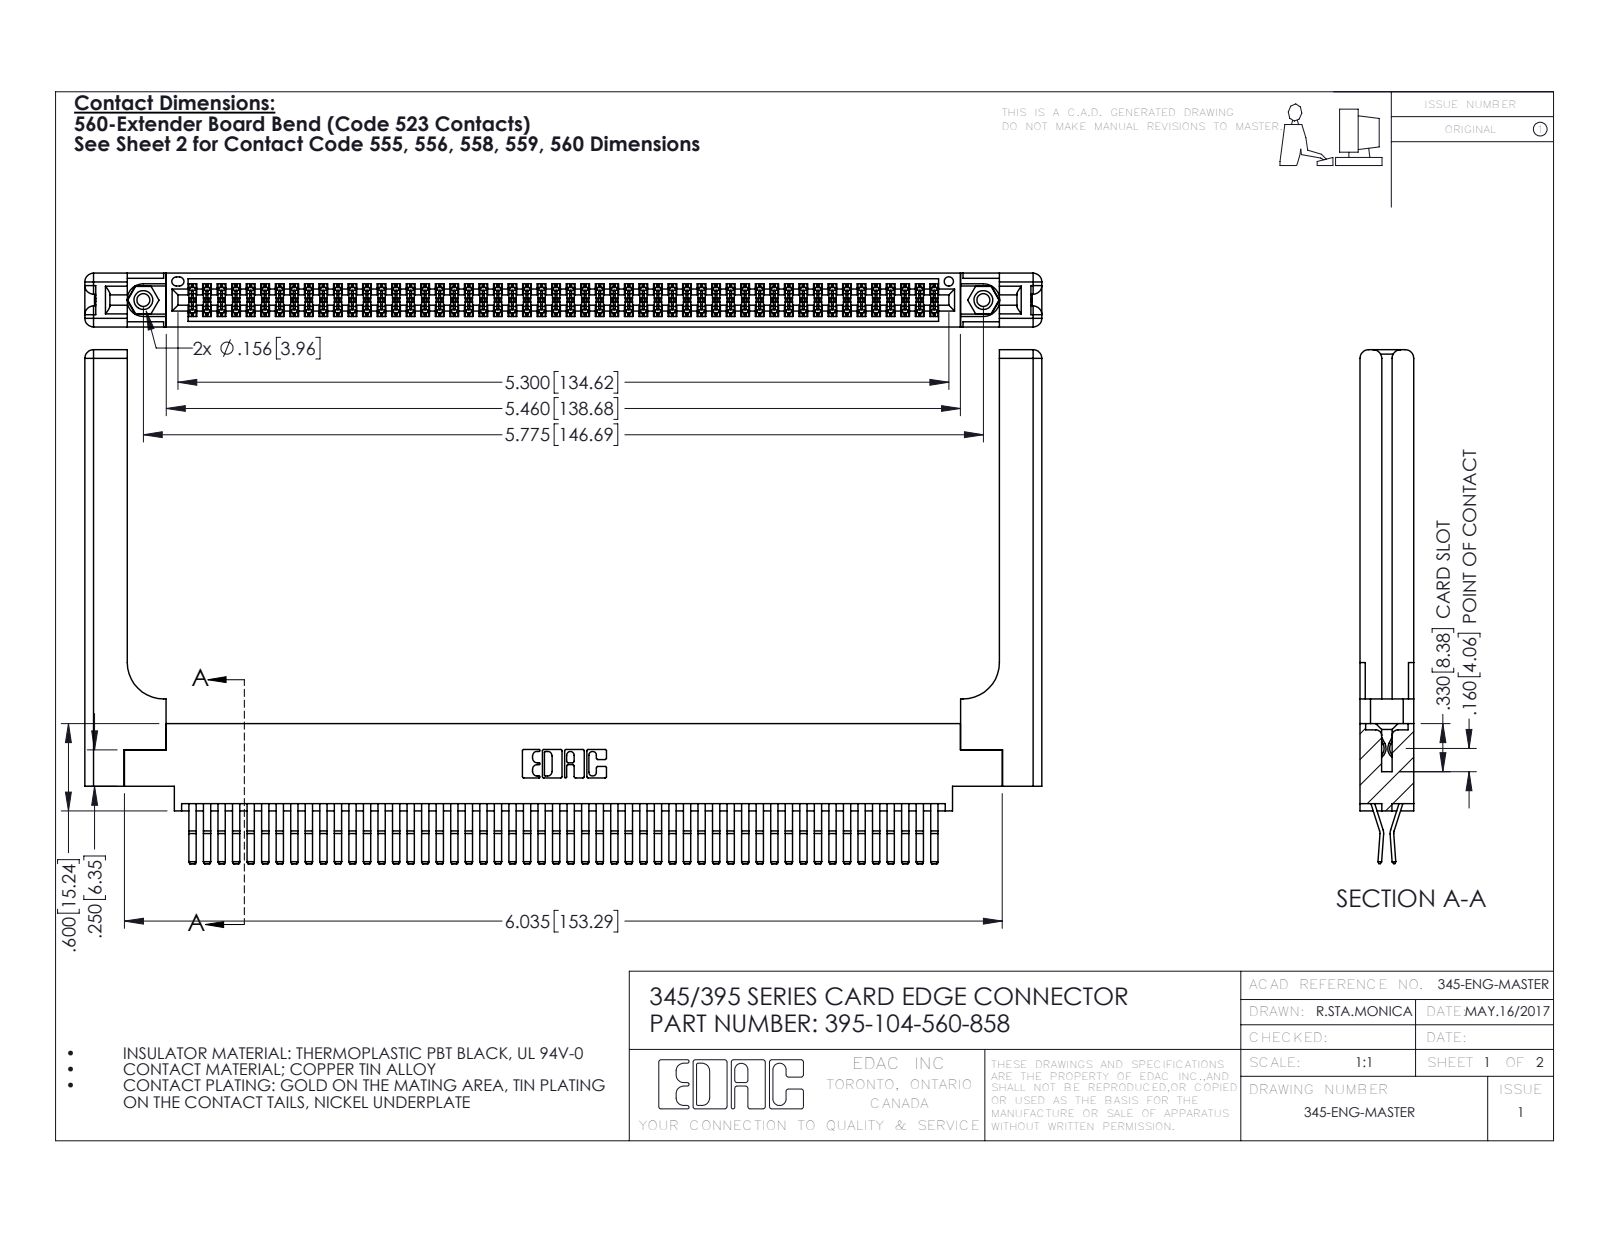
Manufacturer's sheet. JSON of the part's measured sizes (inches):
{"part_name": "345-250-001_345-250-001-102; 345-292-001_560 Tail; 345 Part_0.170 Offset - 0.156 Dia-TH; 395-104-560-858 (+1 more)", "step_written_by": "SolidWorks 2016 (CONFIG_CONTROL_DESIGN)", "units": "inches", "bodies": {"solids": 109, "faces": 5794, "planar": 3664, "cylindrical": 2070, "other": 60}, "overall_size": [6.579, 3.532, 0.37], "volume_in3": 1.548, "surface_area_in2": 49.79, "round_holes": [[0.089, 2], [0.125, 2], [0.156, 2], [0.064, 1]], "round_bosses_or_shafts": [[0.155, 2]], "partial_cylinders_radius": [[0.006, 157], [0.01, 22], [0.06, 16], [0.007, 6], [0.031, 6], [0.026, 3], [0.01, 2], [0.014, 2]], "face_to_face_distances": [0.072, 0.37, 0.298, 0.025, 0.098, 0.272, 0.2, 0.225, 0.175, 0.148], "hole_center_spacings": [0.27, 5.539, 5.775]}
